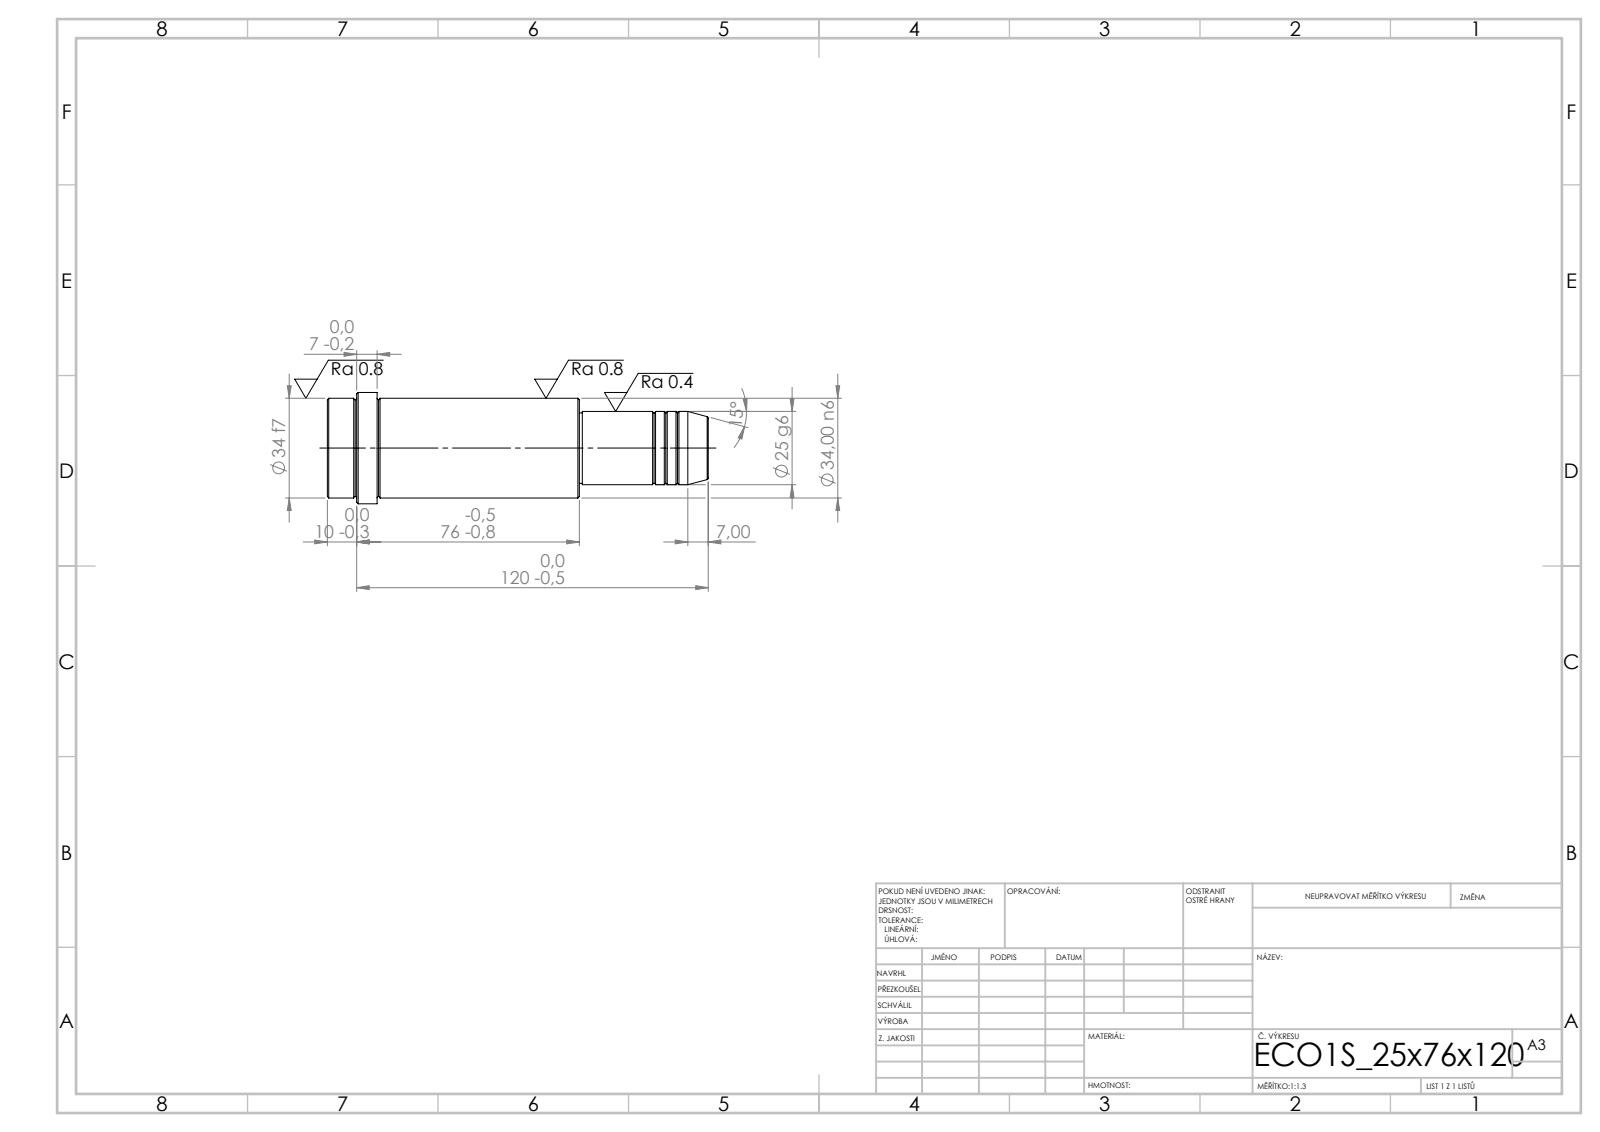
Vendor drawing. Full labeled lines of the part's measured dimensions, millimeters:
STEP written by: SolidWorks 2019 (CONFIG_CONTROL_DESIGN)
Units: millimetres
Bodies: 1 solid, 52 faces (6 planar, 16 cylindrical, 30 other)
Overall size (bounding box): 130 × 38 × 38
Volume: 100 518 mm³ · Surface area: 15 047 mm²
Round bosses / shafts (diameter × count): ⌀38 ×1, ⌀34 ×1, ⌀25 ×1, ⌀24 ×1
Main face-to-face distances: 86, 44, 130, 113, 69, 17, 120, 76, 7, 10
